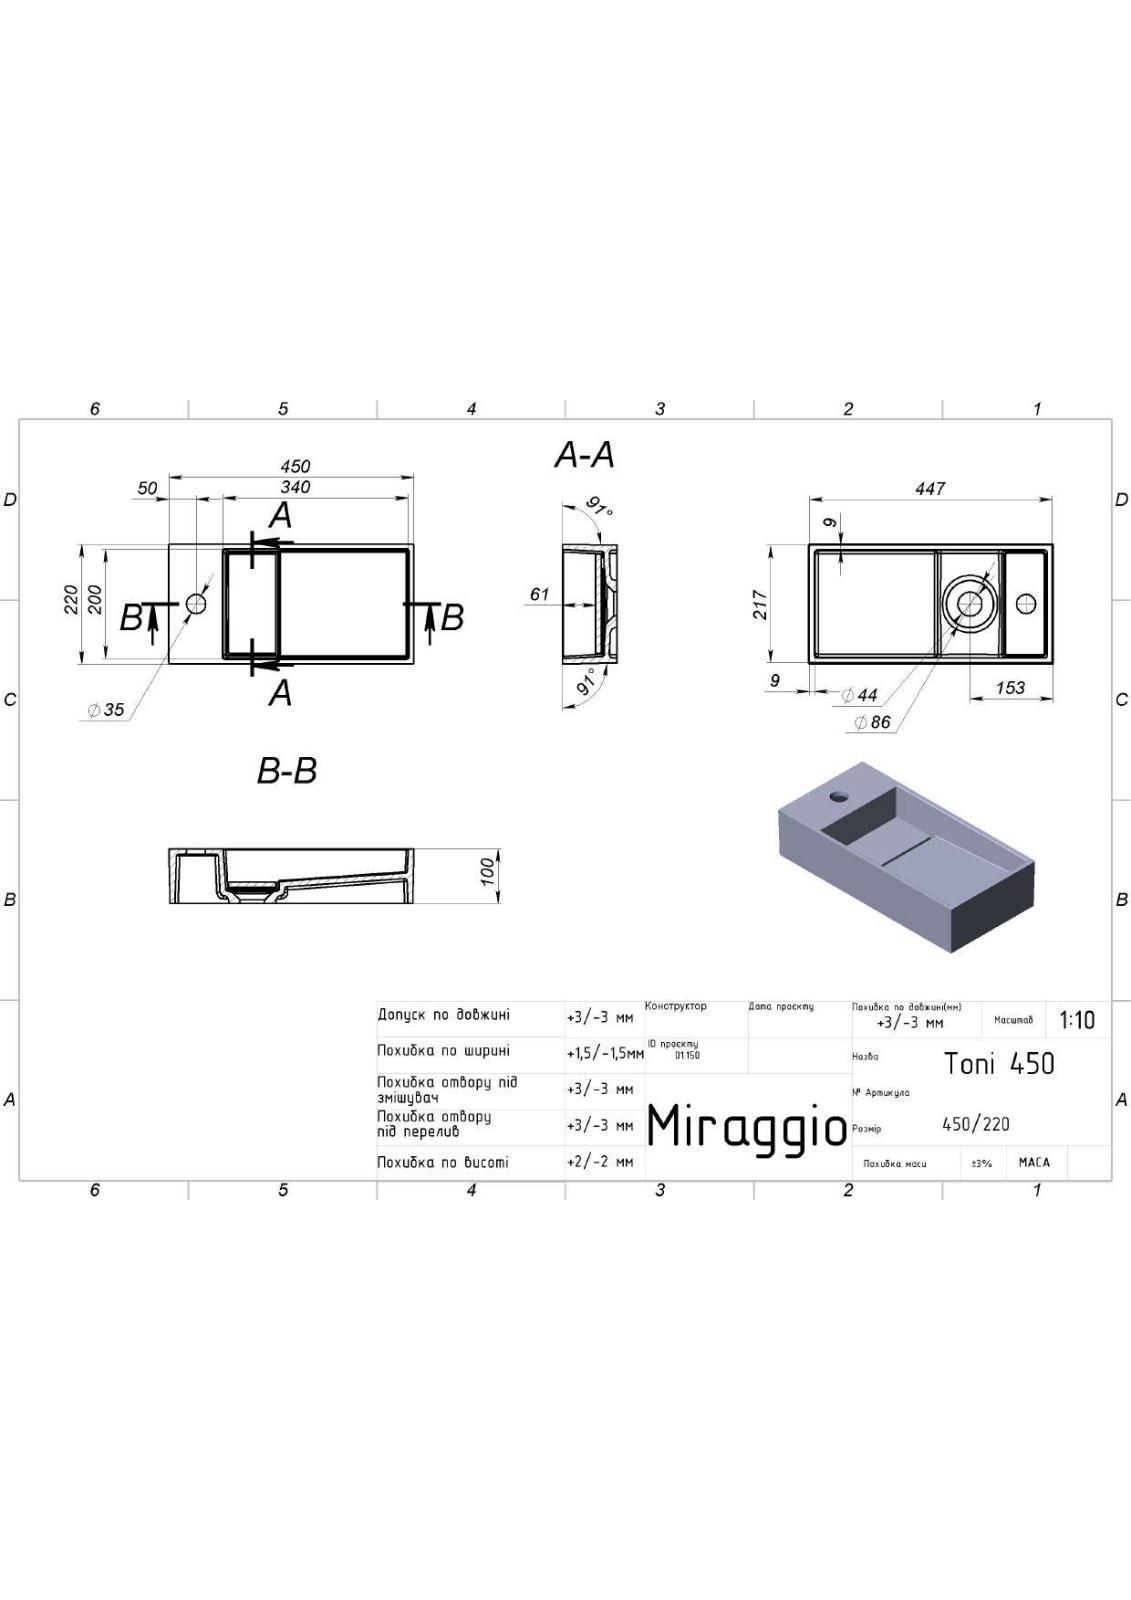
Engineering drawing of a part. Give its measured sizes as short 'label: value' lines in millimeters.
name: Toni 450
written by: SolidWorks 2020 (AUTOMOTIVE_DESIGN)
unit: mm
bodies: 2 solids, 120 faces (30 planar, 40 cylindrical, 50 other)
size: 450 × 220 × 100
volume: 2 601 000 mm³; area: 499 637 mm²
holes: 1× ⌀35, 1× ⌀45
rounds: 16× R2, 12× R6, 6× R4, 4× R3
face distances: 10, 60, 70, 30, 100, 40, 90, 50, 233.49, 88
hole spacings: 103.14
